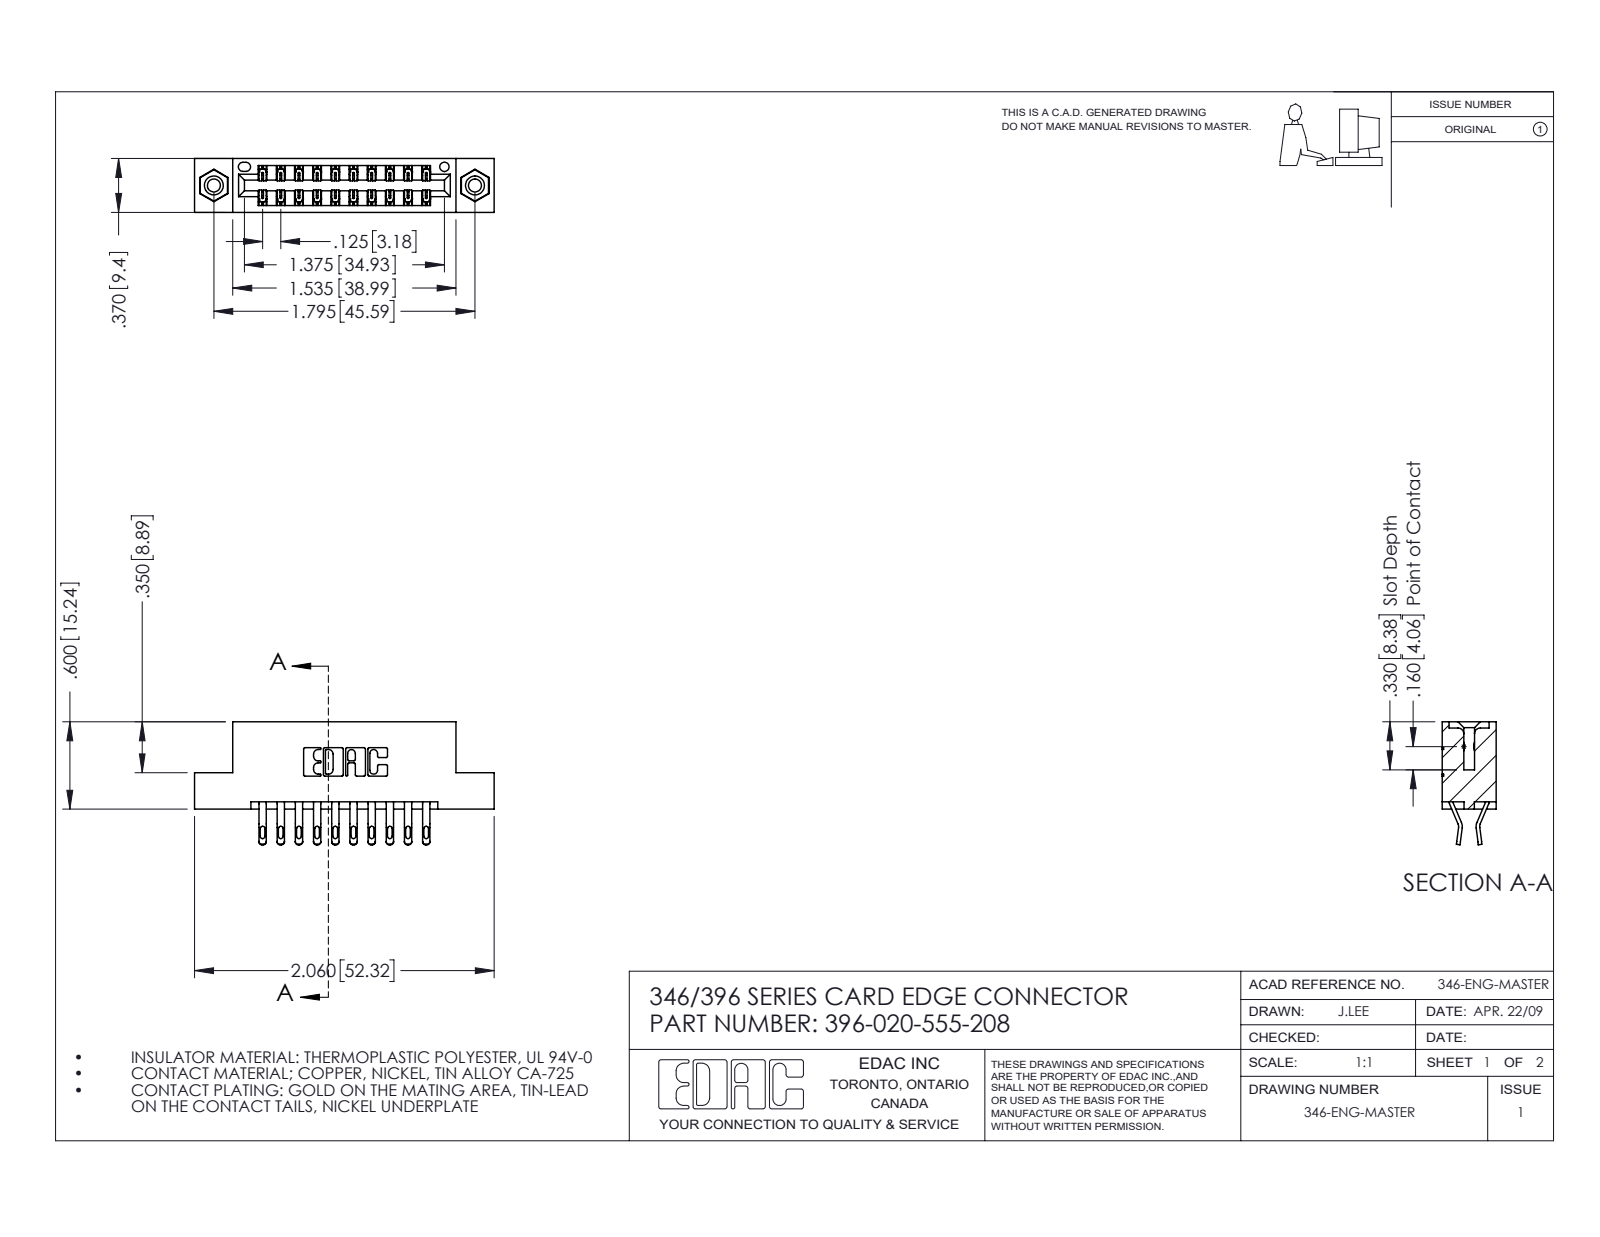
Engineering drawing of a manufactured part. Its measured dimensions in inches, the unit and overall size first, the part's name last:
Units: inches
Overall size (bounding box): 2.06 × 0.845 × 0.37
Round holes (diameter × count): ⌀0.089 ×2, ⌀0.125 ×2, ⌀0.156 ×2, ⌀0.064 ×1
Round bosses / shafts (diameter × count): ⌀0.155 ×2
Partial cylindrical surfaces — rounded edges, fillets, slot ends (radius × count): R0.016 ×40, R0.02 ×40, R0.006 ×30, R0.01 ×22, R0.007 ×6, R0.031 ×6, R0.026 ×3, R0.01 ×2
Main face-to-face distances: 0.25, 0.048, 0.322, 0.37, 0.025, 0.072, 0.298, 0.275, 0.148, 0.222
Hole centre spacings: 0.246, 1.59, 1.795
Volume: 0.299 in³ · Surface area: 10.02 in²
Bodies: 23 solids, 1342 faces (768 planar, 558 cylindrical, 16 other)
Part name (STEP PRODUCT): 345-250-001_345-250-003-102; 345-292-001_555 Tail; 346 Part_Flush Mounting Lugs - 0.156 Dia-TI; 396-020-555-208
STEP written by: SolidWorks 2016 (CONFIG_CONTROL_DESIGN)
